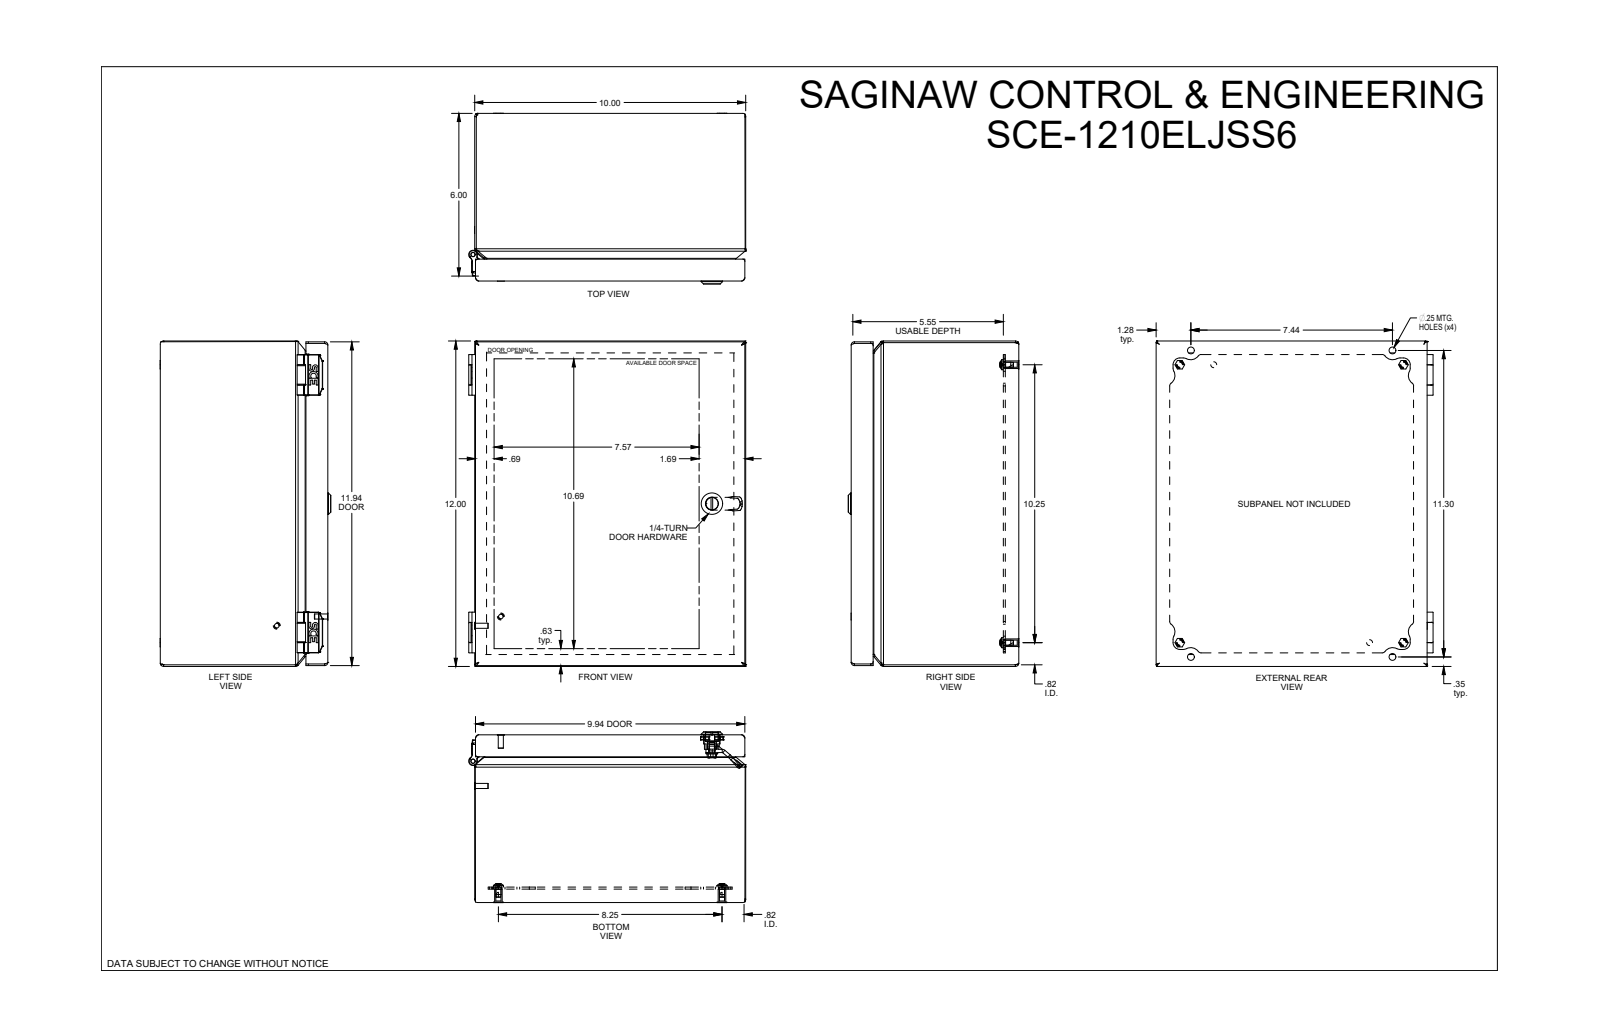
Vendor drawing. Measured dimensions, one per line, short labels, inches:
name: SCE-1210ELJ
written by: SolidWorks 2019 (AUTOMOTIVE_DESIGN)
unit: in
bodies: 34 solids, 1080 faces (395 planar, 349 cylindrical, 336 other)
size: 12.06 × 10.223 × 6.296
volume: 43.08 in³; area: 1 354 in²
holes: 4× ⌀0.17, 4× ⌀0.19, 4× ⌀0.25, 4× ⌀0.284, 3× ⌀0.158, 2× ⌀0.02, 2× ⌀0.1, 2× ⌀0.218, 2× ⌀0.266, 1× ⌀0.196, 1× ⌀0.2, 1× ⌀0.239
bosses: 6× ⌀0.188, 4× ⌀0.479, 4× ⌀0.373, 4× ⌀0.28, 4× ⌀0.16, 2× ⌀0.26, 2× ⌀0.256, 2× ⌀0.237
rounds: 28× R0.03, 24× R0.025, 22× R0.013, 16× R0.05, 14× R0.125, 14× R0.25, 10× R0.01, 10× R0.06
face distances: 0.059, 0.06, 10.001, 6.185, 6.126, 6.066, 6.125, 12.001, 0.571, 0.512
hole spacings: 8.31, 0.06, 1.25, 5.138, 7, 8.25, 9.397, 9.5
